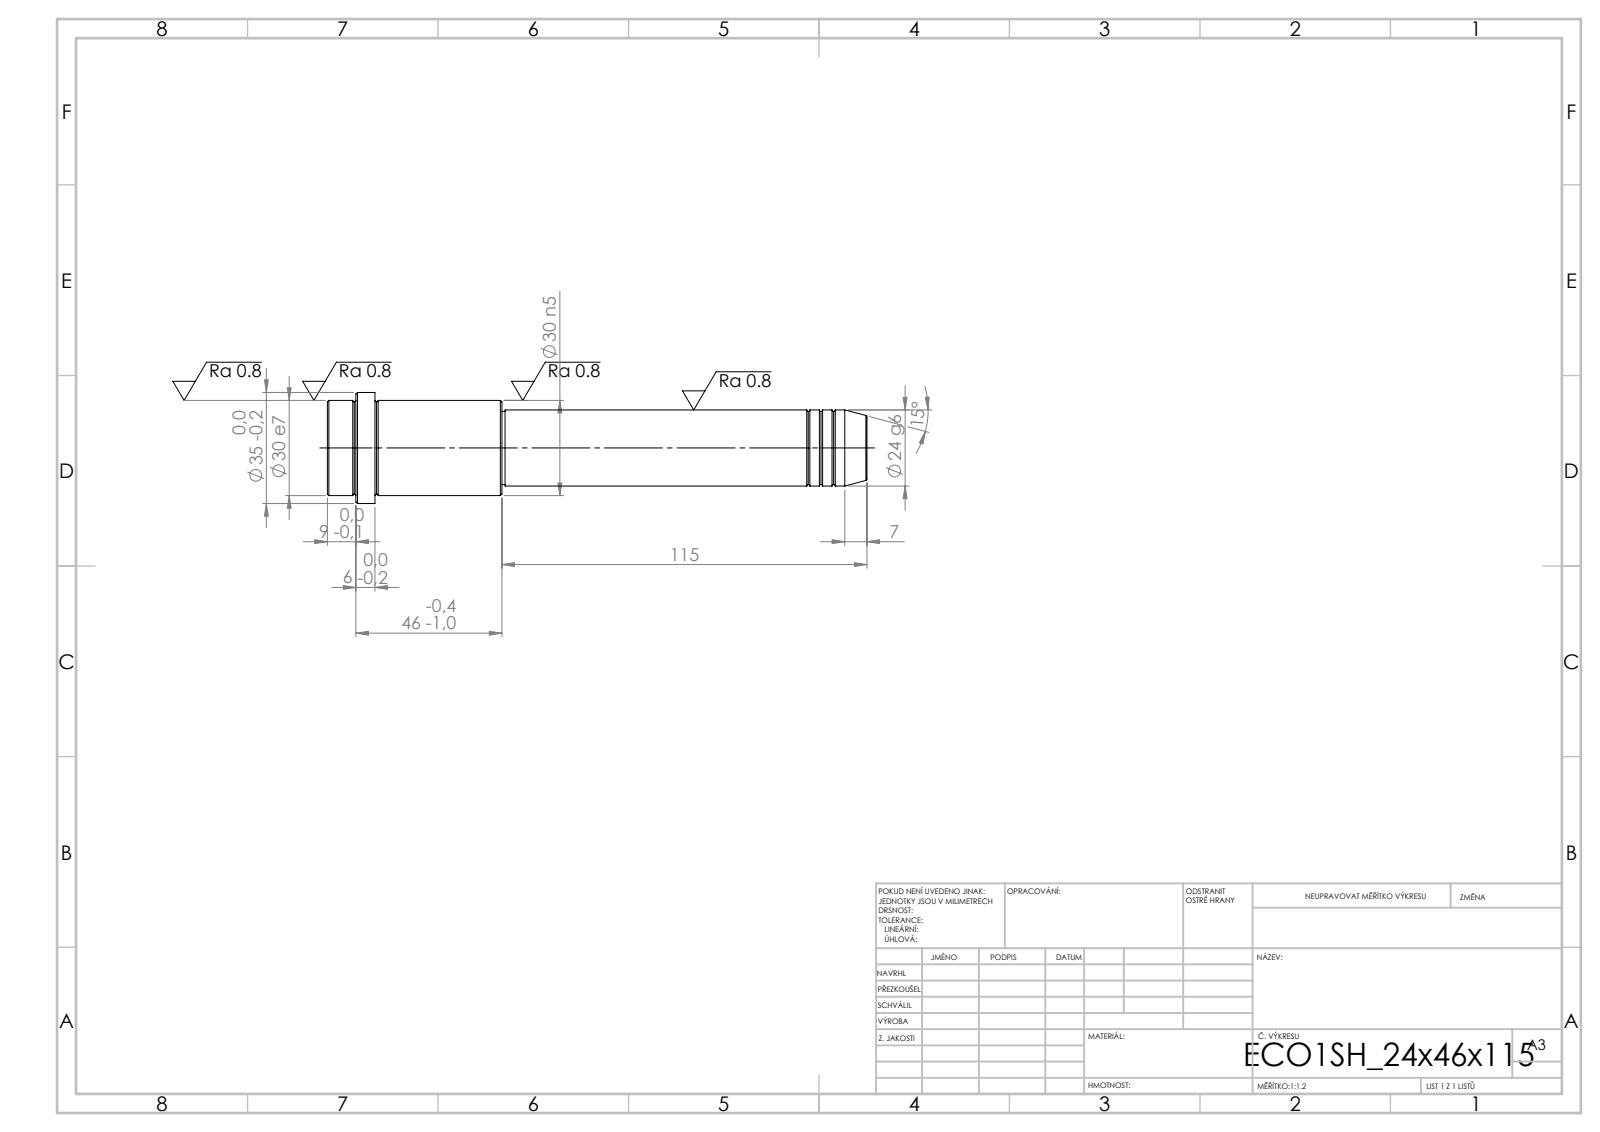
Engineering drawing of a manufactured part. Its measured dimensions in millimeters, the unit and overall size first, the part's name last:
Units: millimetres
Overall size (bounding box): 170 × 35 × 35
Round bosses / shafts (diameter × count): ⌀35 ×1, ⌀30 ×1, ⌀24 ×1, ⌀23 ×1
Main face-to-face distances: 170, 155, 15, 115, 40, 55, 161, 46, 6, 9
Volume: 91 728 mm³ · Surface area: 15 914 mm²
Bodies: 1 solid, 52 faces (6 planar, 16 cylindrical, 30 other)
STEP written by: SolidWorks 2019 (CONFIG_CONTROL_DESIGN)
